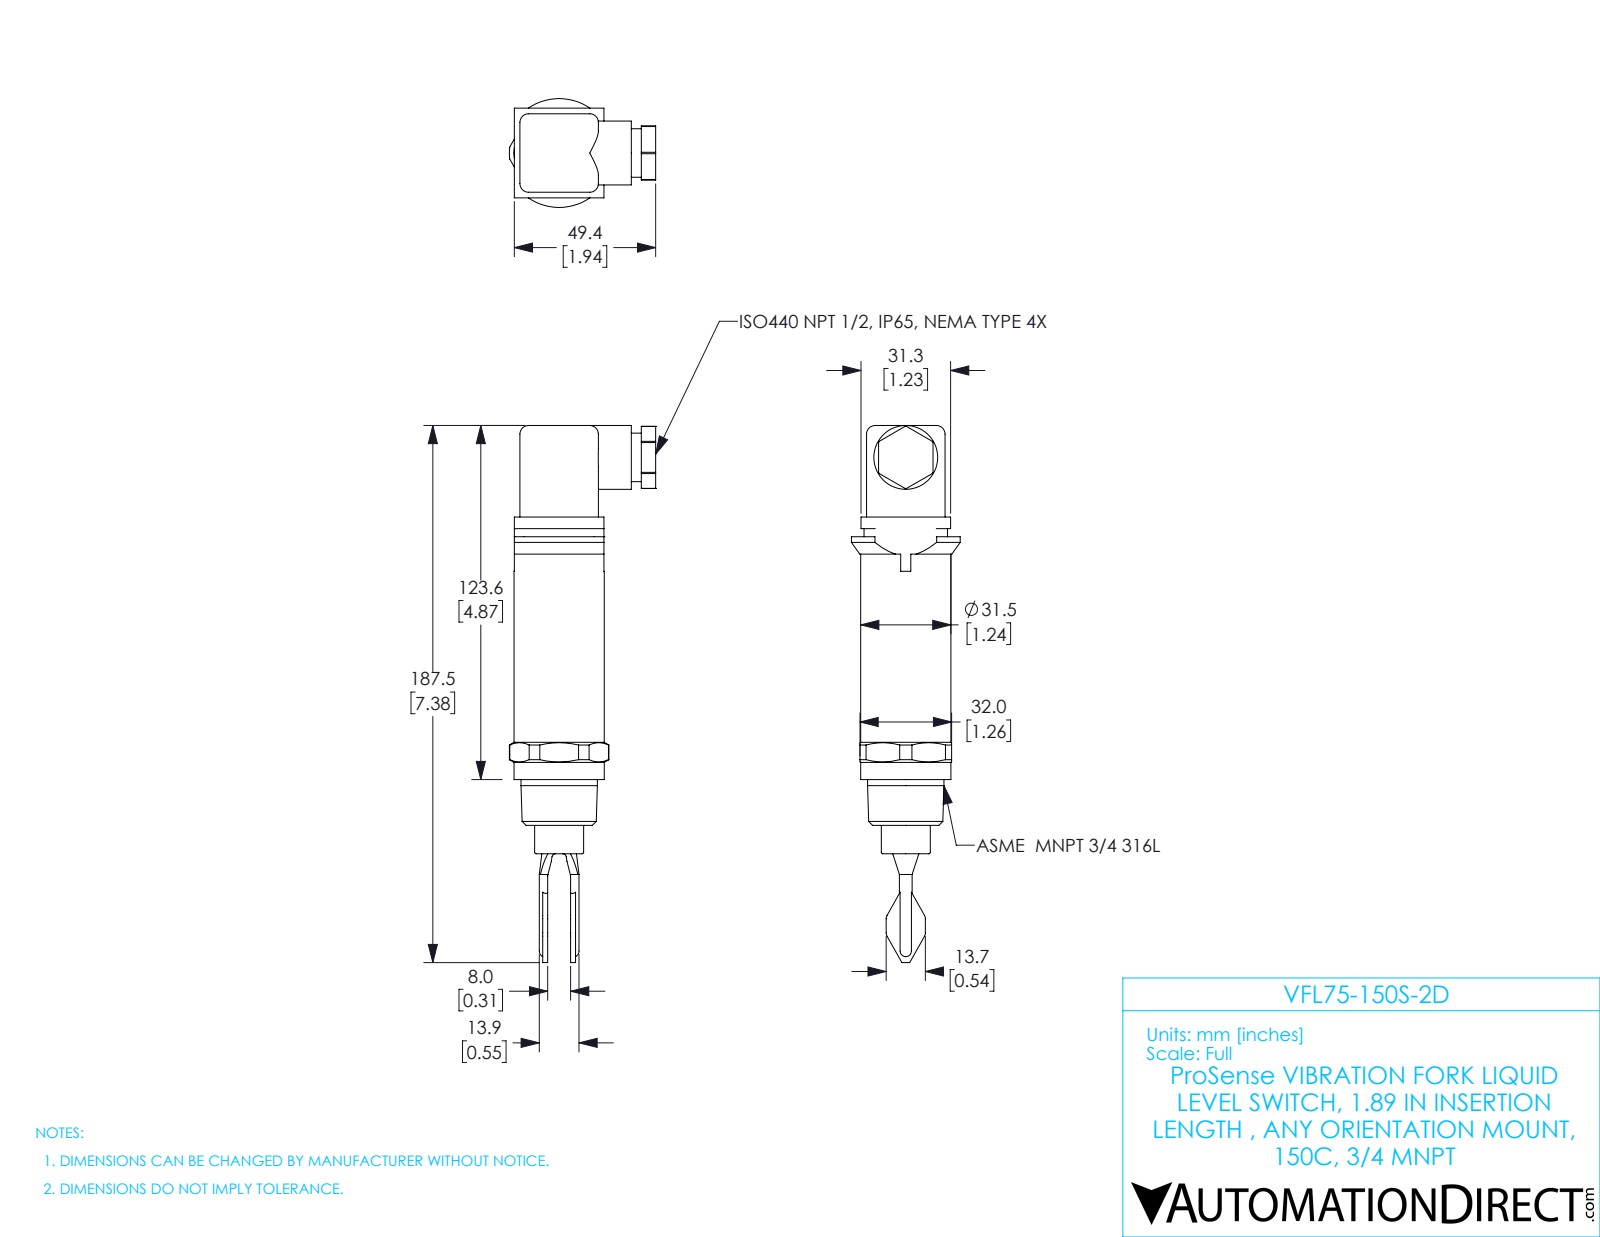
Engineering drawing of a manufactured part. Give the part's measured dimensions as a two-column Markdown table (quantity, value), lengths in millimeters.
| quantity | value |
| --- | --- |
| part name | VFL75-150S-2D |
| STEP written by | SolidWorks 2017 (AUTOMOTIVE_DESIGN) |
| units | millimeters |
| bodies | 1 solid, 155 faces (78 planar, 56 cylindrical, 21 other) |
| overall size | 187.5 × 51.1 × 38 |
| volume | 117 000 mm³ |
| surface area | 19 570 mm² |
| round bosses / shafts (diameter × count) | 31.5 × 1, 26.7 × 1, 22.3 × 1, 17.1 × 1, 16.9 × 1 |
| partial cylindrical surfaces (radius × count) | 3 × 8, 1.2 × 4, 2.4 × 4, 3.9 × 4, 2.2 × 2, 10.8 × 1, 17.4 × 1, 19 × 1 |
| main face-to-face distances | 27.4, 2, 29.4, 11.7, 19.7, 9.7, 17.7, 31.3, 29.7, 49.4 |
